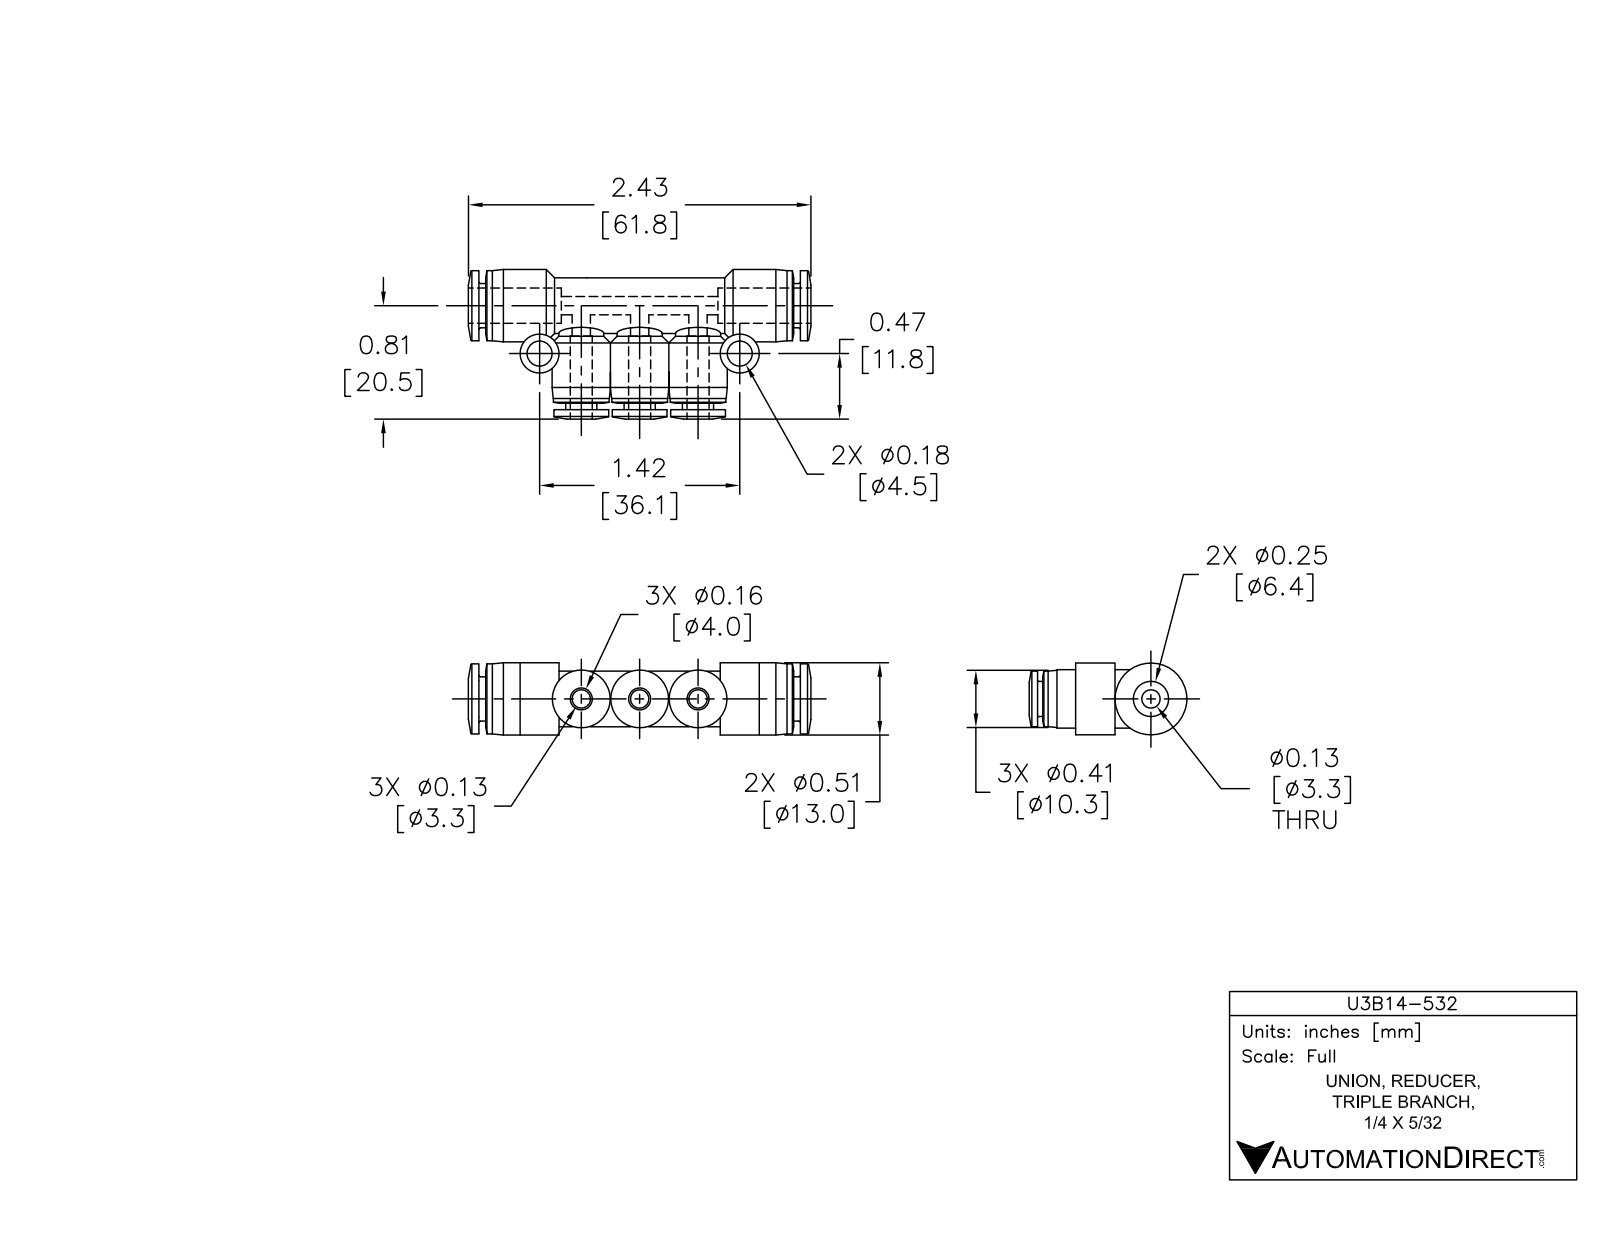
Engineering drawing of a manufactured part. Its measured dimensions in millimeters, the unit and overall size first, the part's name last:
Units: millimetres
Overall size (bounding box): 61.6 × 26.9 × 13
Round holes (diameter × count): ⌀3.2 ×4, ⌀4.3 ×3, ⌀4.5 ×2, ⌀6.6 ×1
Round bosses / shafts (diameter × count): ⌀10 ×4, ⌀10.5 ×3, ⌀9.9 ×3, ⌀8.1 ×3, ⌀5.6 ×3, ⌀7 ×2, ⌀13 ×1, ⌀12.6 ×1
Main face-to-face distances: 1.1, 57.8, 1.2, 56.6, 14.9, 42.9, 13.7, 41.7, 13, 55.4
Hole centre spacings: 10.5, 21, 36
Volume: 8 110 mm³ · Surface area: 6 968 mm²
Bodies: 1 solid, 173 faces (22 planar, 77 cylindrical, 74 other)
Part name (STEP PRODUCT): U3B14-532
STEP written by: SolidWorks 2015 (AUTOMOTIVE_DESIGN)
